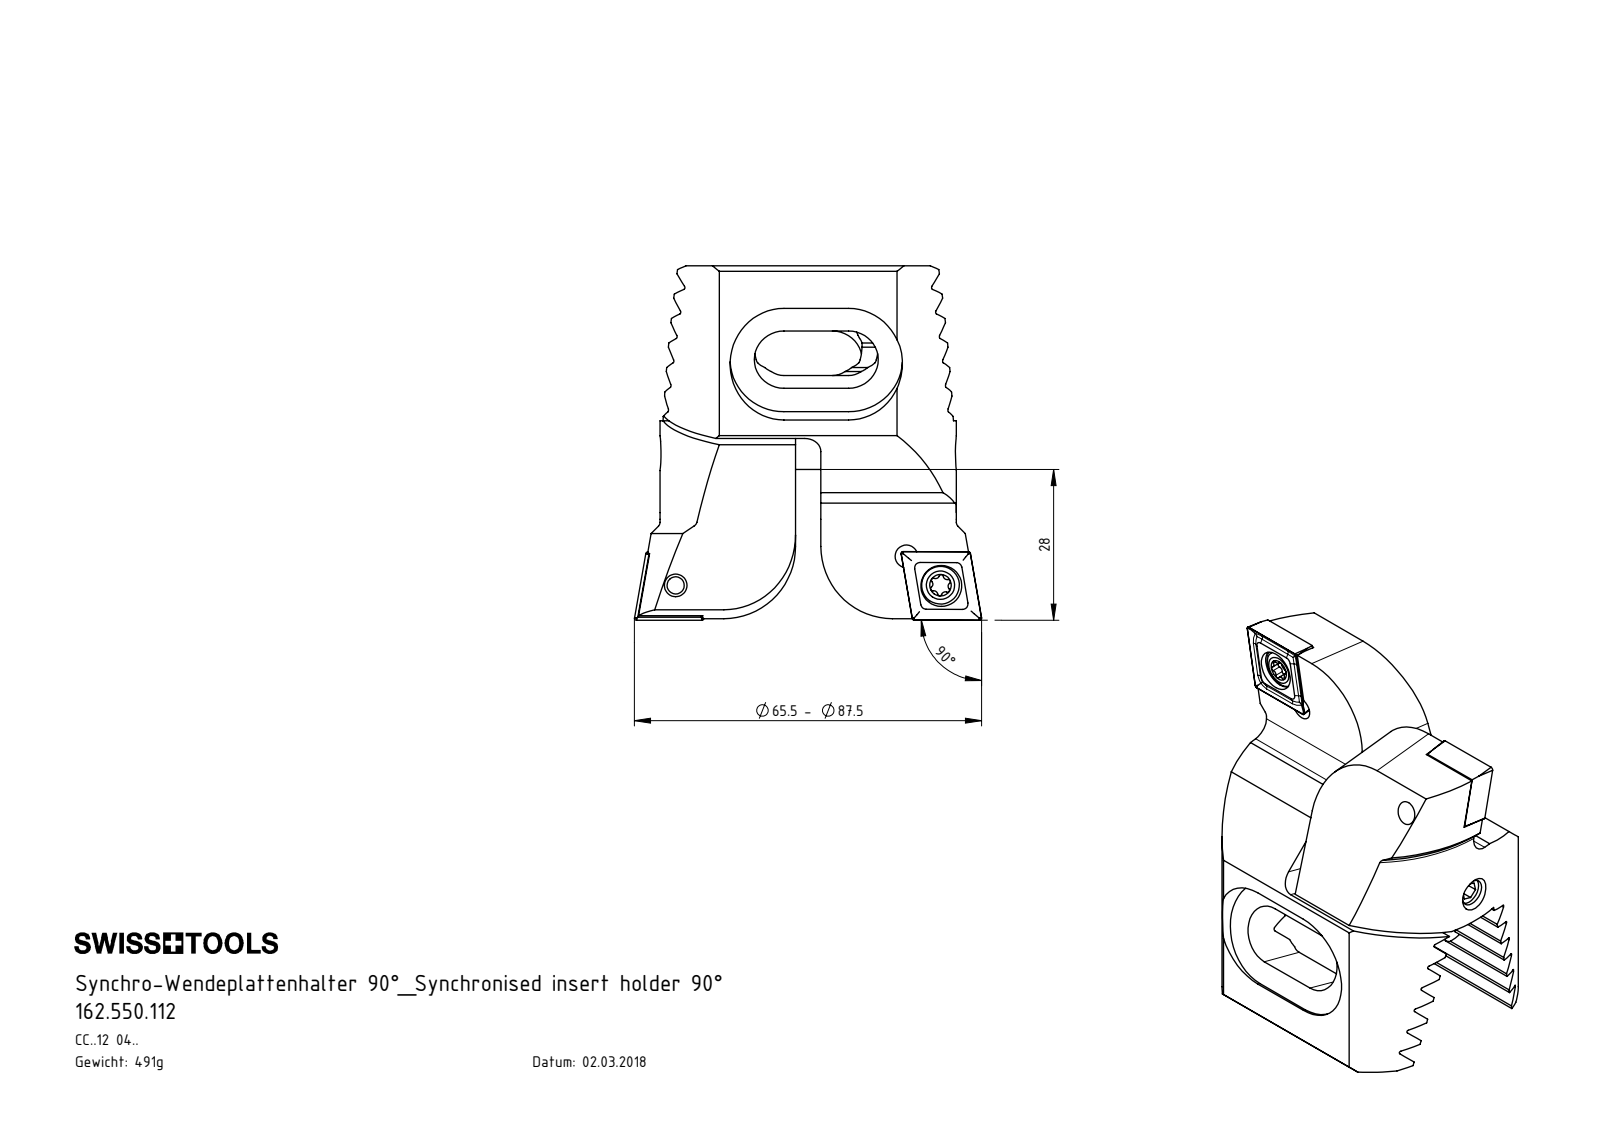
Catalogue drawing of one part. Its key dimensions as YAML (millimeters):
part_name: "Z55-WCC.001.037_A; Z55-ER3.001.052_A; CCMT120404; Z55-WCC.003.037_A (+4 more)"
step_written_by: "SolidWorks 2017 (CONFIG_CONTROL_DESIGN)"
units: millimeters
bodies: {solids: 11, faces: 484, planar: 187, cylindrical: 155, other: 142}
overall_size: [65.75, 64.42, 44]
volume: 62568
surface_area: 24121
round_holes:
  - {diameter: 4.2, count: 4}
  - {diameter: 1, count: 3}
  - {diameter: 3.3, count: 3}
  - {diameter: 5.5, count: 2}
  - {diameter: 7.6, count: 2}
  - {diameter: 5, count: 1}
round_bosses_or_shafts:
  - {diameter: 4, count: 3}
  - {diameter: 7, count: 2}
  - {diameter: 5, count: 2}
  - {diameter: 17, count: 1}
  - {diameter: 6, count: 1}
  - {diameter: 3.8, count: 1}
partial_cylinders:
  - {radius: 0.34, count: 12}
  - {radius: 0.39, count: 12}
  - {radius: 0.69, count: 12}
  - {radius: 1, count: 8}
  - {radius: 3, count: 4}
  - {radius: 5.5, count: 4}
  - {radius: 10, count: 4}
  - {radius: 13.3, count: 2}
face_to_face_distances: [4.07, 8.14, 12.21, 16.28, 20.35, 4.85, 17.24, 1, 7.12, 21.7]
hole_center_spacings: [8.29, 3, 8.49, 8.5, 14.99, 15, 15.3, 28.36]
